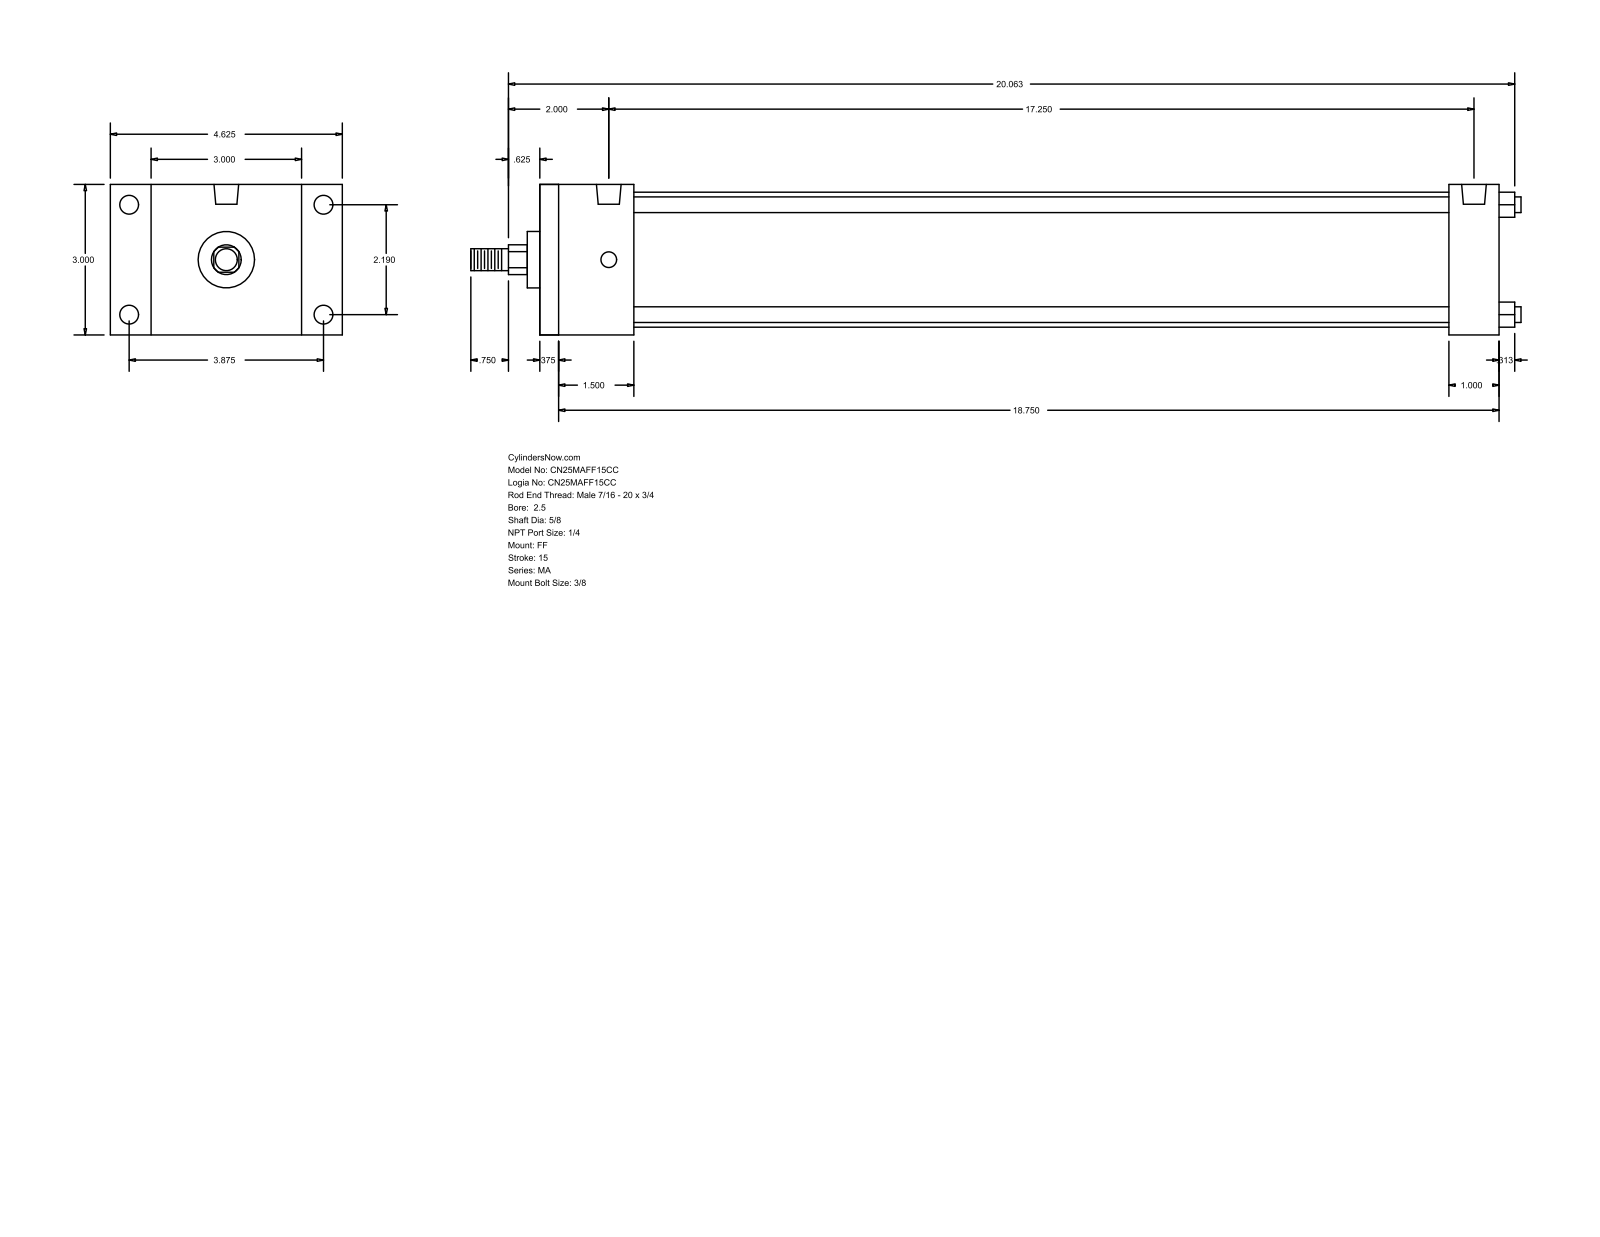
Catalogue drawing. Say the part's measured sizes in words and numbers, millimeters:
The part is named "MA_FF__0250_0.625". Its 3-D file was written by "GSSL Pune (CONFIG_CONTROL_DESIGN)". It is 0 solids with 92 faces: 64 planar, 28 cylindrical and 0 other. Overall it measures 531.81 by 117.47 by 76.2 millimeters. Round holes: 4 of diameter 7.94, 4 of diameter 9.53, 2 of diameter 12.49. Round bosses or shafts: 4 of diameter 7.94, 1 of diameter 68.33, 1 of diameter 28.57, 1 of diameter 15.88, 1 of diameter 11.11. Partial cylindrical surfaces (rounded edges, fillets, slot ends): 1 of radius 7.54. The main face-to-face distances are 76.2, 485.77, 476.25, 9.52, 25.4, 47.62, 460.37, 38.1, 450.85, 412.75. The hole center spacings are 55.62, 98.42, 113.05, 438.15.
